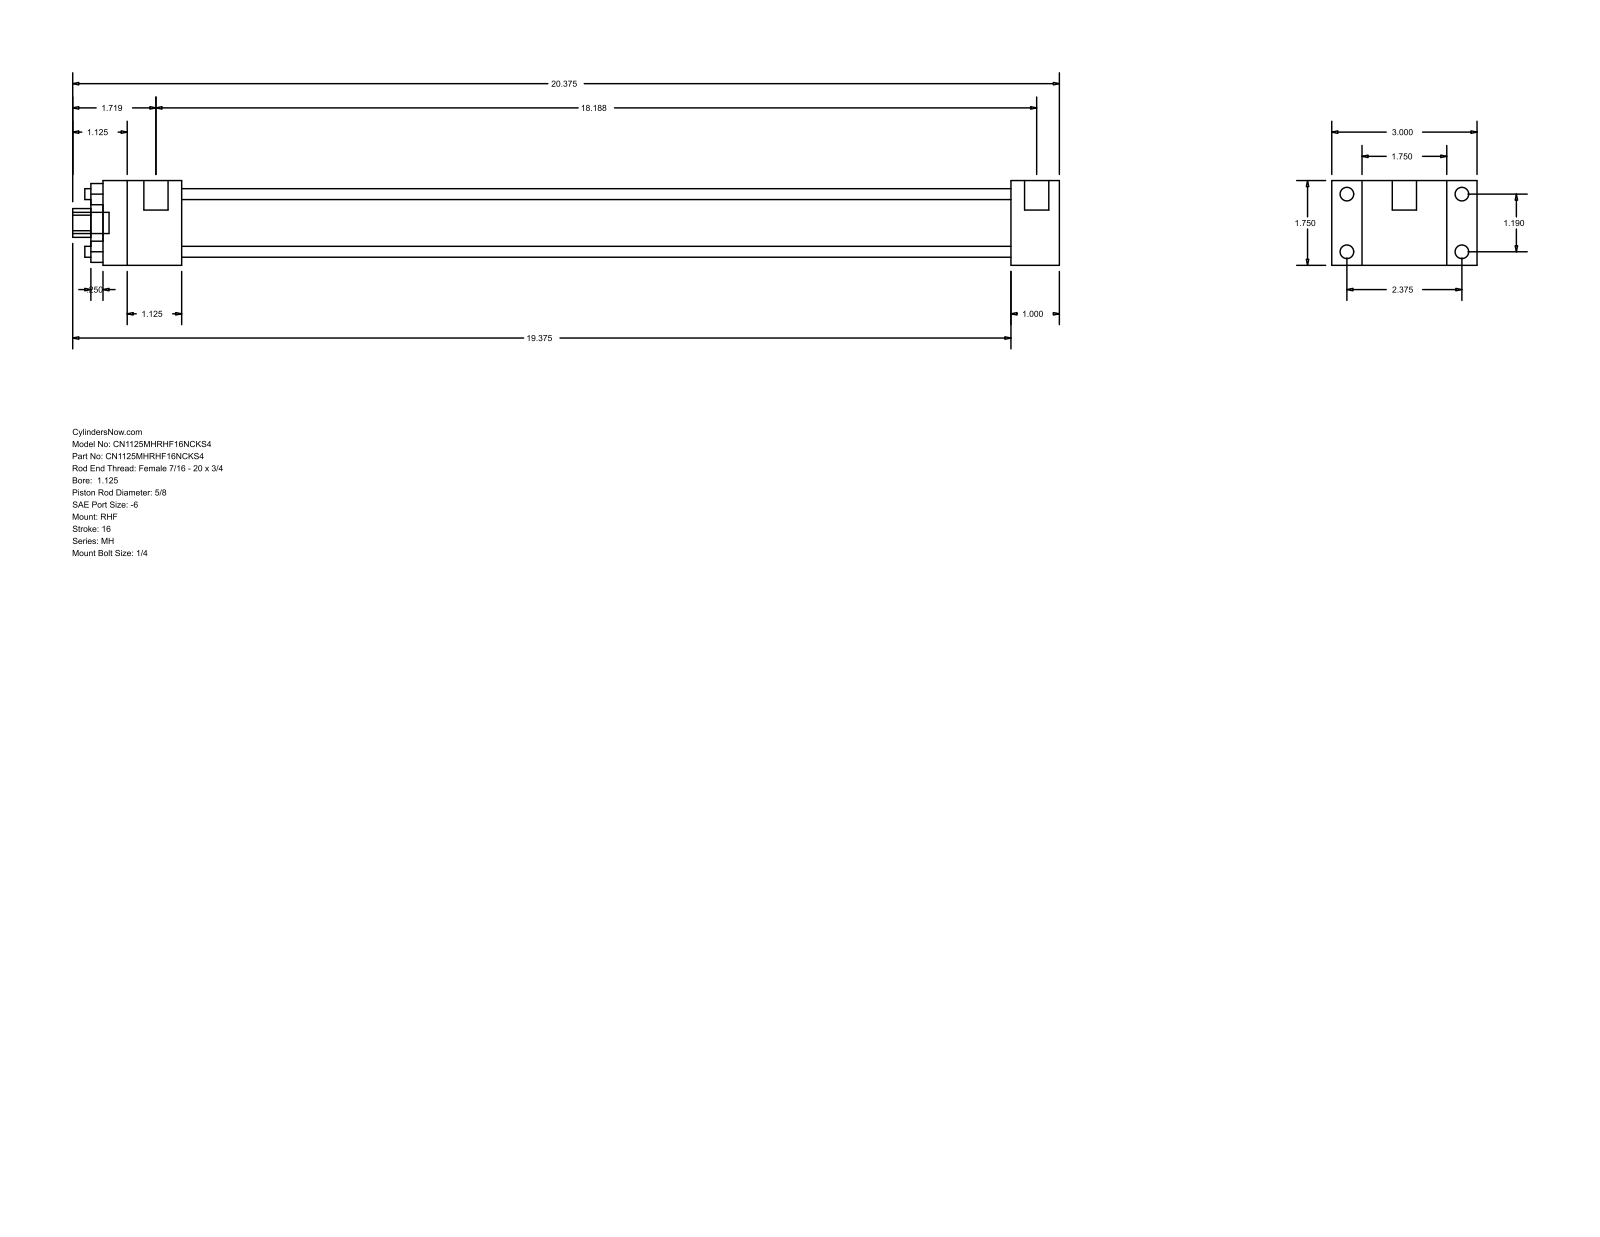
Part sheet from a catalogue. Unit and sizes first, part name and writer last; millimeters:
Units: millimetres
Overall size (bounding box): 517.52 × 76.2 × 44.45
Round holes (diameter × count): ⌀5.71 ×4, ⌀15.88 ×1, ⌀28.57 ×1, ⌀34.92 ×1
Round bosses / shafts (diameter × count): ⌀7.14 ×4, ⌀5.56 ×4, ⌀12.7 ×2, ⌀11.11 ×1
Partial cylindrical surfaces — rounded edges, fillets, slot ends (radius × count): R7.54 ×1
Main face-to-face distances: 44.46, 15.87, 60.33, 25.4, 76.2, 434.97, 460.37, 41.27, 476.24, 501.64
Hole centre spacings: 21.37, 30.22, 42.74
Bodies: 0 solids, 88 faces (60 planar, 28 cylindrical, 0 other)
Part name (STEP PRODUCT): MH_RHF__0112_0.625
STEP written by: GSSL Pune (CONFIG_CONTROL_DESIGN)
